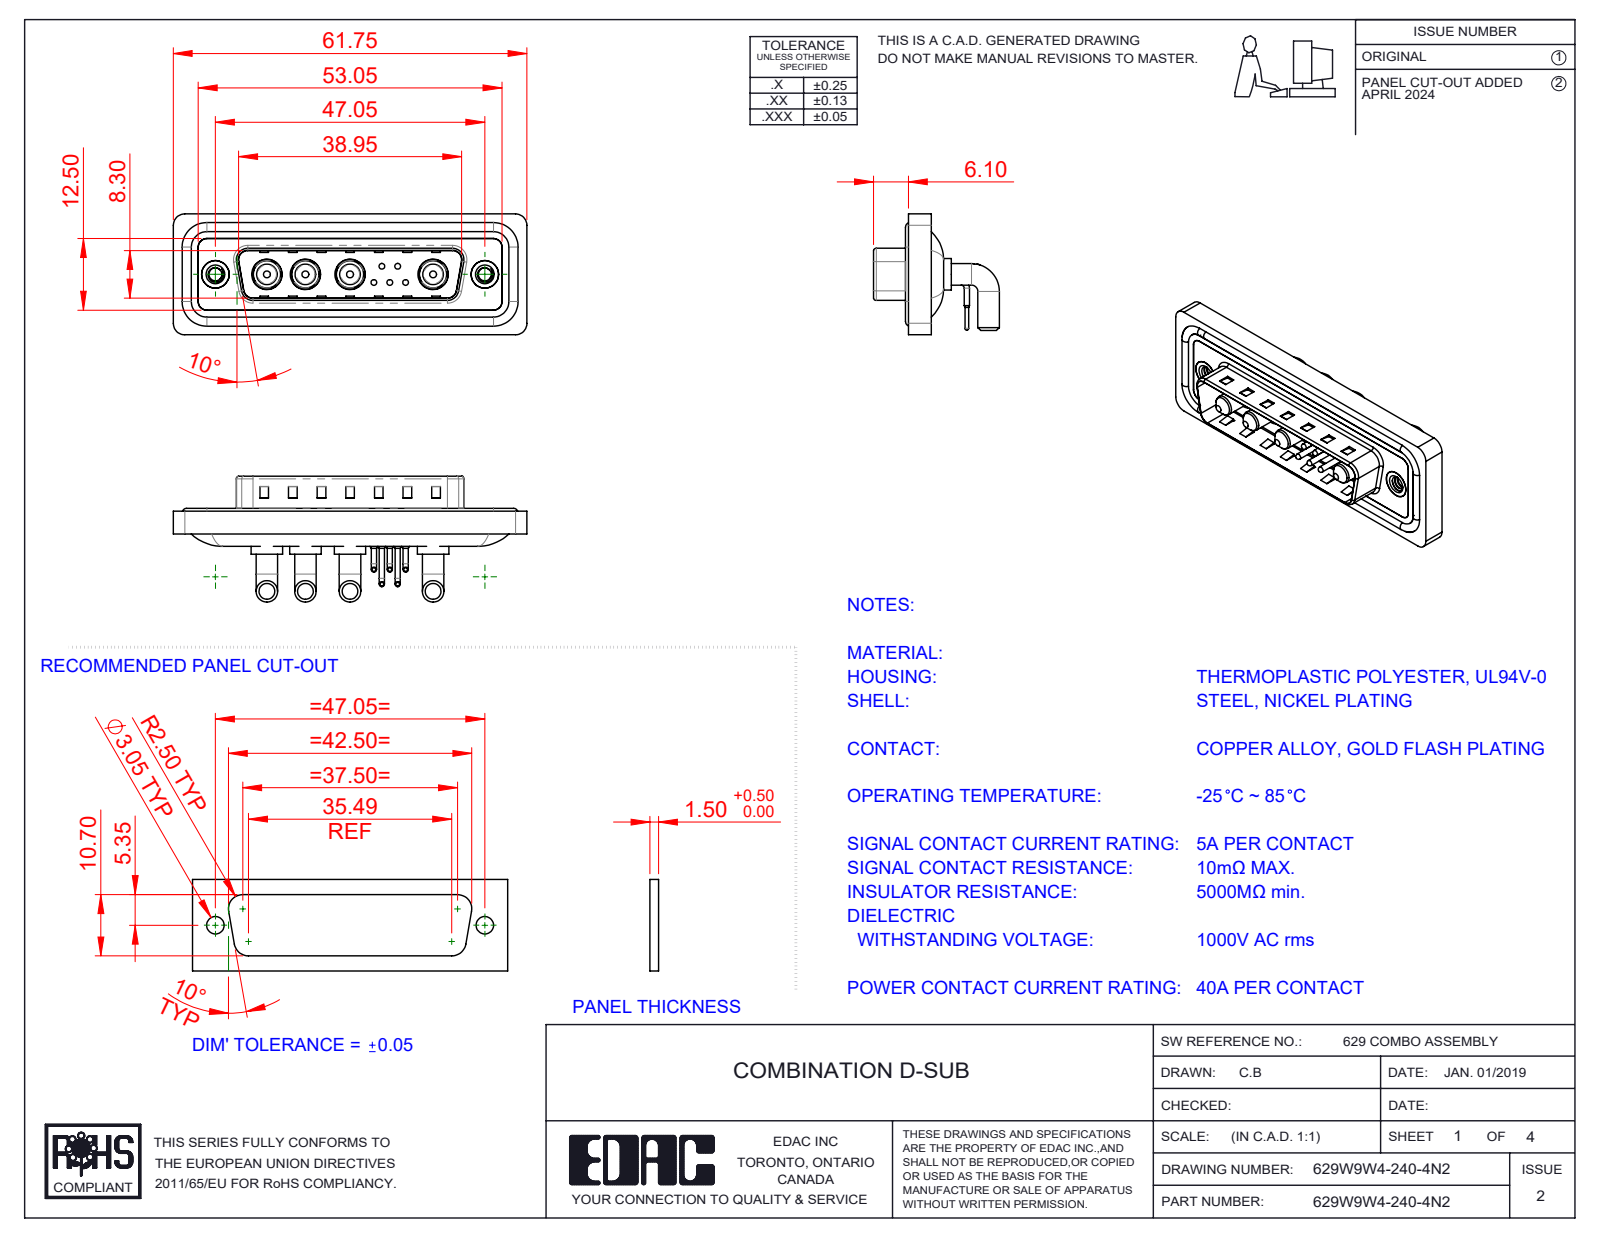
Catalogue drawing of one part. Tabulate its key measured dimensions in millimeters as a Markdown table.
| quantity | value |
| --- | --- |
| part name | 629Combo Contact Row 1; 629Combo Shell Front_25 Contacts; 629Combo Threaded Rivet_2; 629Combo Contact Row 2 (+5 more) |
| STEP written by | SolidWorks 2023 (CONFIG_CONTROL_DESIGN) |
| units | millimeters |
| bodies | 20 solids, 1205 faces (569 planar, 452 cylindrical, 184 other) |
| overall size | 61.75 × 21.98 × 21.1 |
| volume | 8 007 mm³ |
| surface area | 12 552 mm² |
| round holes (diameter × count) | 0.75 × 5, 1.6 × 5, 2 × 5, 4.85 × 4, 5.3 × 4, 2.26 × 2, 4 × 2, 4.8 × 2, 5 × 2 |
| round bosses / shafts (diameter × count) | 0.9 × 10, 3.75 × 8, 1.5 × 5, 1 × 5, 0.65 × 5, 5.5 × 4, 5.2 × 4, 4.75 × 4 |
| partial cylindrical surfaces (radius × count) | 1.5 × 18, 2 × 18, 0.5 × 8, 1.6 × 8, 1.01 × 5, 0.25 × 4, 0.6 × 4, 0.65 × 4 |
| main face-to-face distances | 0.4, 2.9, 0.8, 4.1, 1.1, 4.5, 2.1, 1.6, 3.1, 6 |
| hole center spacings | 3.16, 2.77, 5.04, 14.5, 2.78, 4.4, 4.41, 5 |
